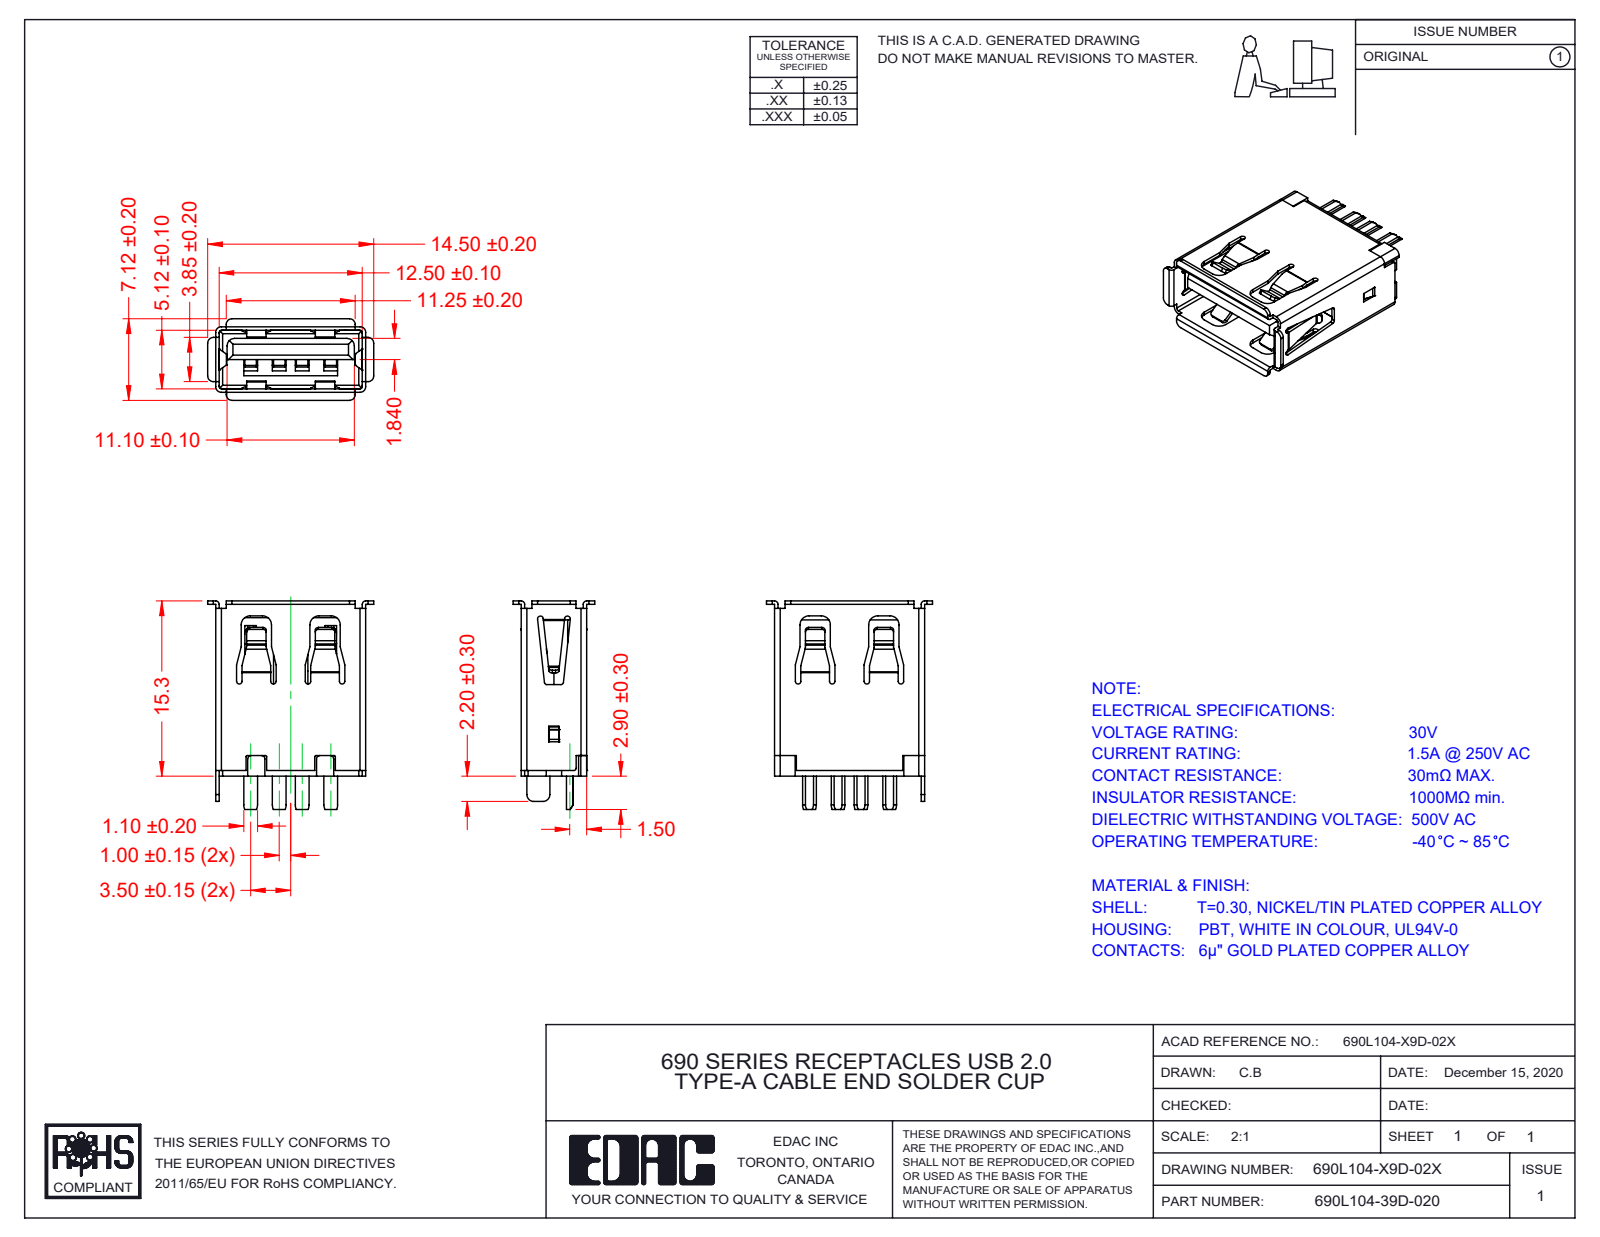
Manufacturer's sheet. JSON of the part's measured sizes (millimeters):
{"part_name": "Contact 690L104-X9D-02X; Insulator 2 690L104-X9D-02X_White; 690L104-19D-020; Insulator 690L104-X9D-02X_White (+1 more)", "step_written_by": "SolidWorks 2020 (AUTOMOTIVE_DESIGN)", "units": "millimeters", "bodies": {"solids": 7, "faces": 790, "planar": 558, "cylindrical": 184, "other": 48}, "overall_size": [18.2, 14.5, 7.12], "volume_mm3": 618, "surface_area_mm2": 2270, "partial_cylinders_radius": [[0.3, 19], [0.5, 19], [0.1, 16], [0.2, 12], [0.6, 9], [0.27, 8], [0.25, 6], [0.4, 6]], "face_to_face_distances": [5.42, 2.55, 5.12, 5.72, 5.41, 0.31, 5.11, 2.86, 2.56, 12.8]}
